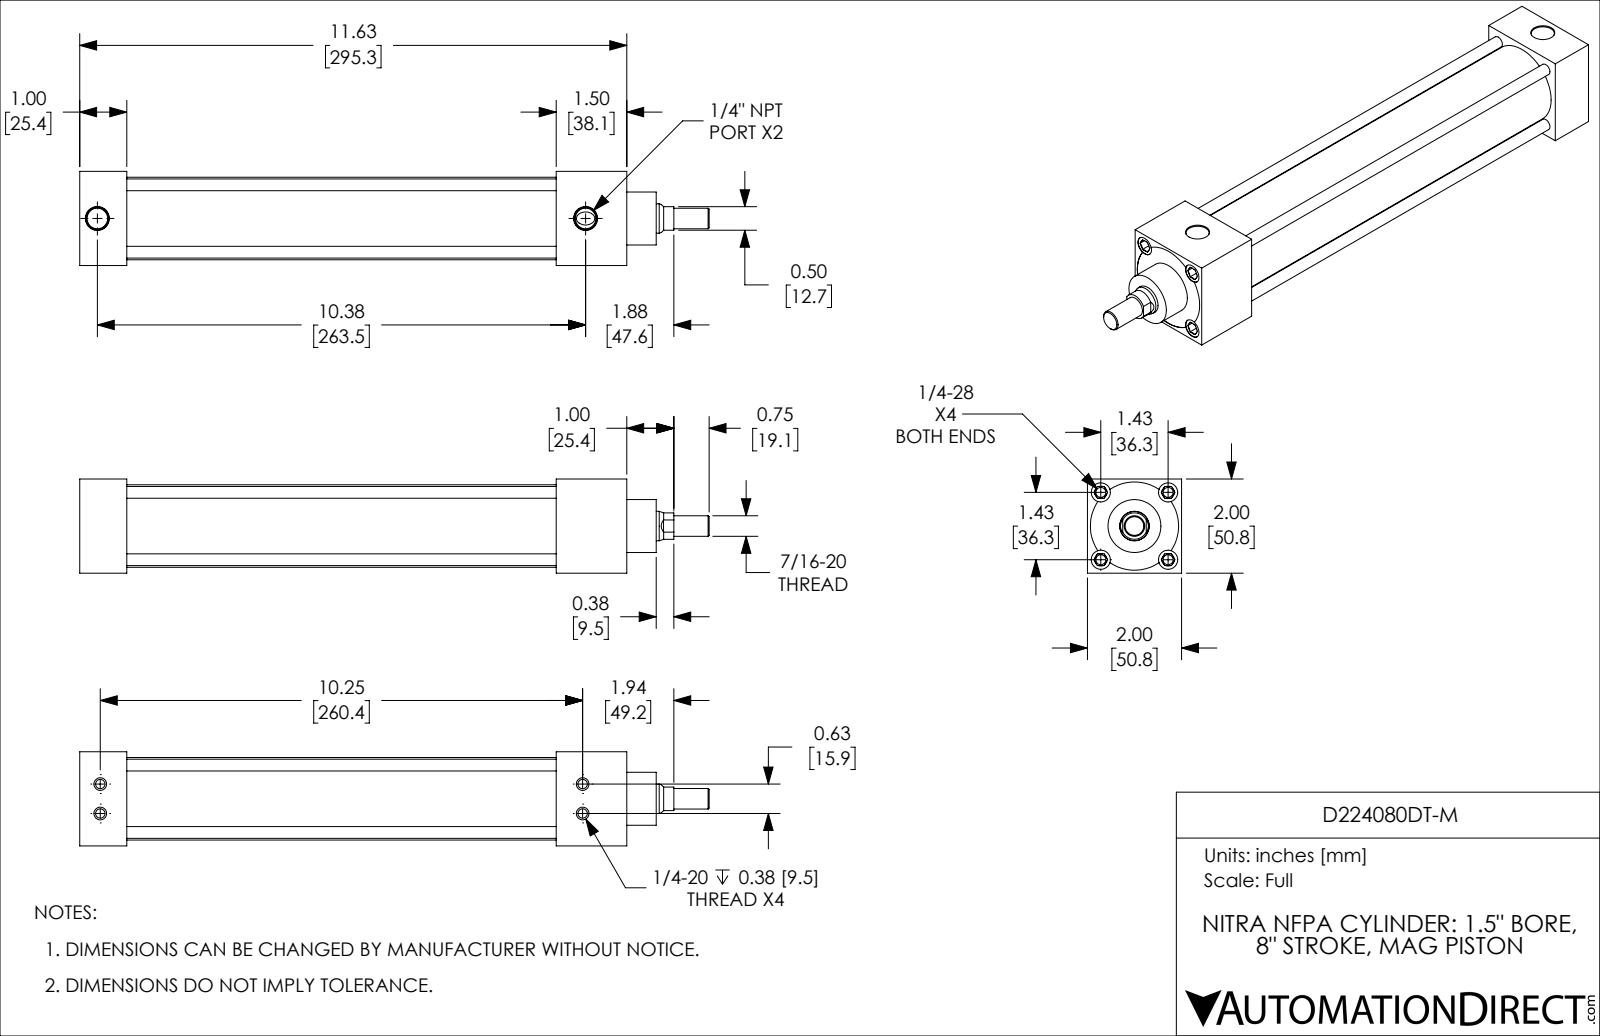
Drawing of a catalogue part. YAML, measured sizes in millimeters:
part_name: "D224080DT-M_PISTON_KK1; D224080DT-M; D224080DT-M_BODY"
step_written_by: "SolidWorks 2019 (CONFIG_CONTROL_DESIGN)"
units: millimeters
bodies: {solids: 2, faces: 203, planar: 58, cylindrical: 65, other: 80}
overall_size: [339.7, 50.8, 50.8]
volume: 365400
surface_area: 128900
round_holes:
  - {diameter: 5.1, count: 4}
  - {diameter: 5.4, count: 4}
  - {diameter: 10.3, count: 4}
  - {diameter: 11.1, count: 2}
  - {diameter: 15.9, count: 1}
  - {diameter: 38.1, count: 1}
round_bosses_or_shafts:
  - {diameter: 6.4, count: 4}
  - {diameter: 44.5, count: 1}
  - {diameter: 38.1, count: 1}
  - {diameter: 28.6, count: 1}
  - {diameter: 15.8, count: 1}
  - {diameter: 11.1, count: 1}
partial_cylinders:
  - {radius: 7.1, count: 1}
  - {radius: 23.8, count: 1}
face_to_face_distances: [50.8, 25.4, 257.2, 231.8, 54, 295.1, 269.7, 38, 28.6, 203.2]
hole_center_spacings: [8.1, 25.7, 36.3, 15.9, 51.4, 260.4, 260.8, 262.1]
